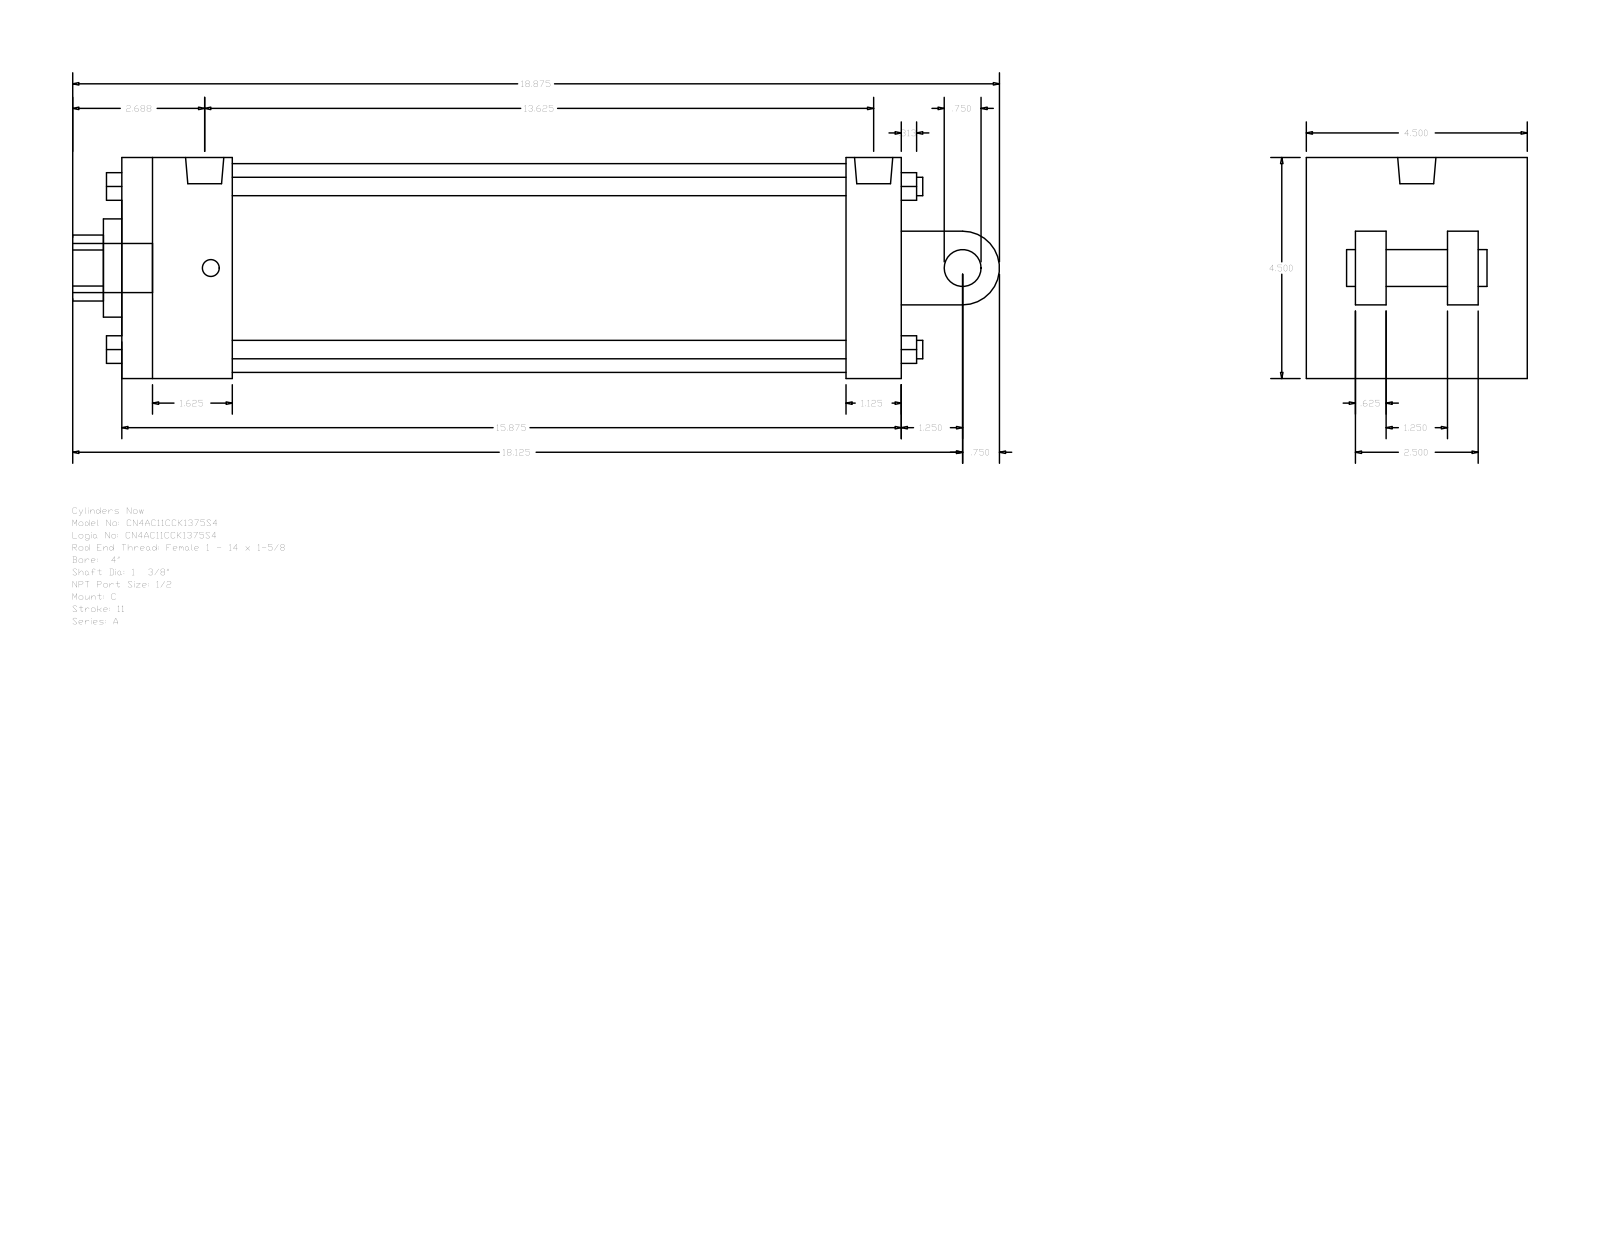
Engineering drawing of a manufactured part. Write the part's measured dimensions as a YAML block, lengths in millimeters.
part_name: "A_C__0400_1.375"
step_written_by: "GSSL Pune (CONFIG_CONTROL_DESIGN)"
units: millimeters
bodies: {solids: 0, faces: 135, planar: 102, cylindrical: 33, other: 0}
overall_size: [479.43, 114.3, 114.3]
round_holes:
  - {diameter: 8.73, count: 2}
  - {diameter: 19.77, count: 1}
  - {diameter: 34.92, count: 1}
  - {diameter: 50.8, count: 1}
  - {diameter: 107.95, count: 1}
round_bosses_or_shafts:
  - {diameter: 9.53, count: 4}
  - {diameter: 8.73, count: 2}
  - {diameter: 25.4, count: 1}
  - {diameter: 19.77, count: 1}
  - {diameter: 19.05, count: 1}
partial_cylinders:
  - {radius: 17.06, count: 1}
  - {radius: 19.05, count: 1}
face_to_face_distances: [114.3, 403.22, 73.03, 28.57, 374.65, 57.15, 317.5, 346.07, 15.87, 41.27]
hole_center_spacings: [3.18]
